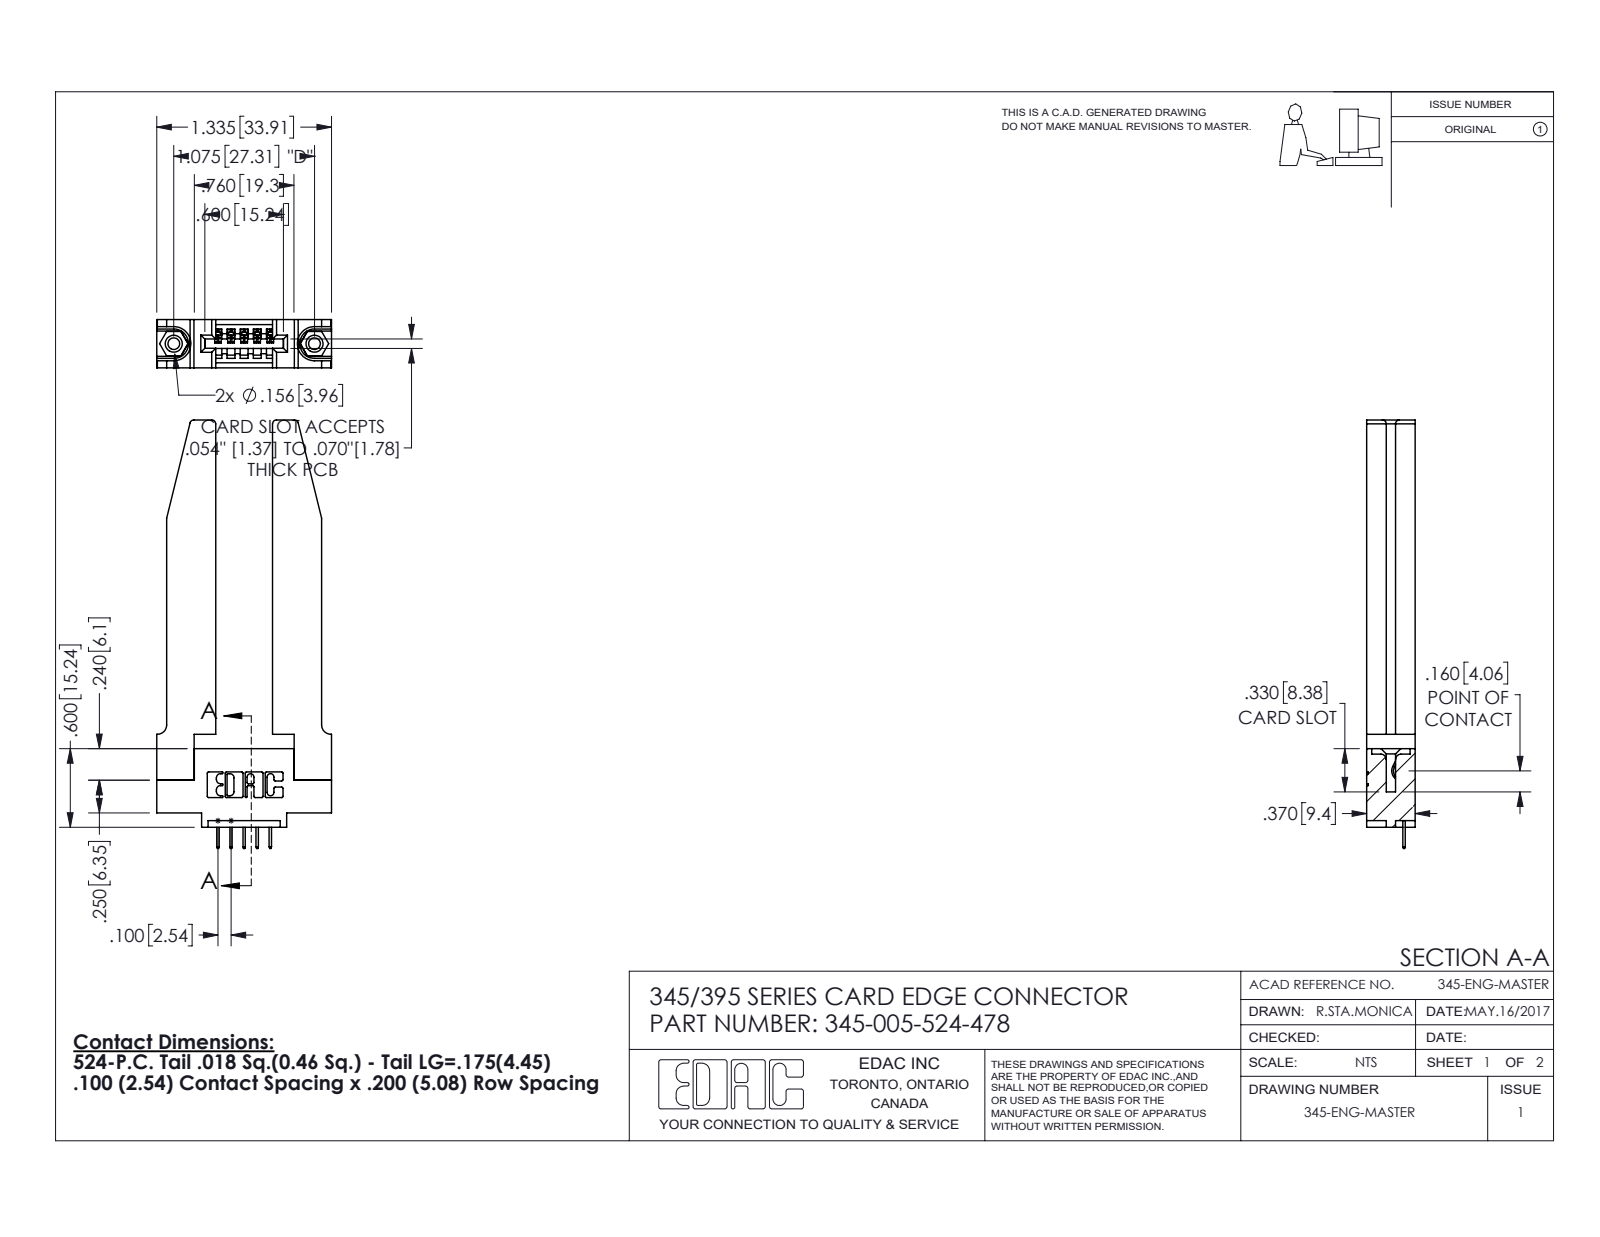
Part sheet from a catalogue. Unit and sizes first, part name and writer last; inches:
Units: inches
Overall size (bounding box): 3.272 × 1.336 × 0.37
Round holes (diameter × count): ⌀0.089 ×2, ⌀0.125 ×2, ⌀0.156 ×2, ⌀0.064 ×1
Round bosses / shafts (diameter × count): ⌀0.155 ×2
Partial cylindrical surfaces — rounded edges, fillets, slot ends (radius × count): R0.01 ×22, R0.006 ×10, R0.03 ×8, R0.007 ×6, R0.031 ×6, R0.026 ×3, R0.031 ×2, R0.04 ×2
Main face-to-face distances: 0.37, 0.15, 0.22, 0.435, 0.072, 0.148, 0.298, 0.077, 0.071, 0.055
Hole centre spacings: 0.27, 0.847, 1.075
Volume: 0.647 in³ · Surface area: 15.68 in²
Bodies: 10 solids, 674 faces (456 planar, 166 cylindrical, 52 other)
Part name (STEP PRODUCT): 345-220-078_345-220-078; 345-250-001_345-250-001-102; 345 Part_0.110 Offset - 0.156 Dia-TH; 345-005-524-478 (+1 more)
STEP written by: SolidWorks 2016 (CONFIG_CONTROL_DESIGN)
